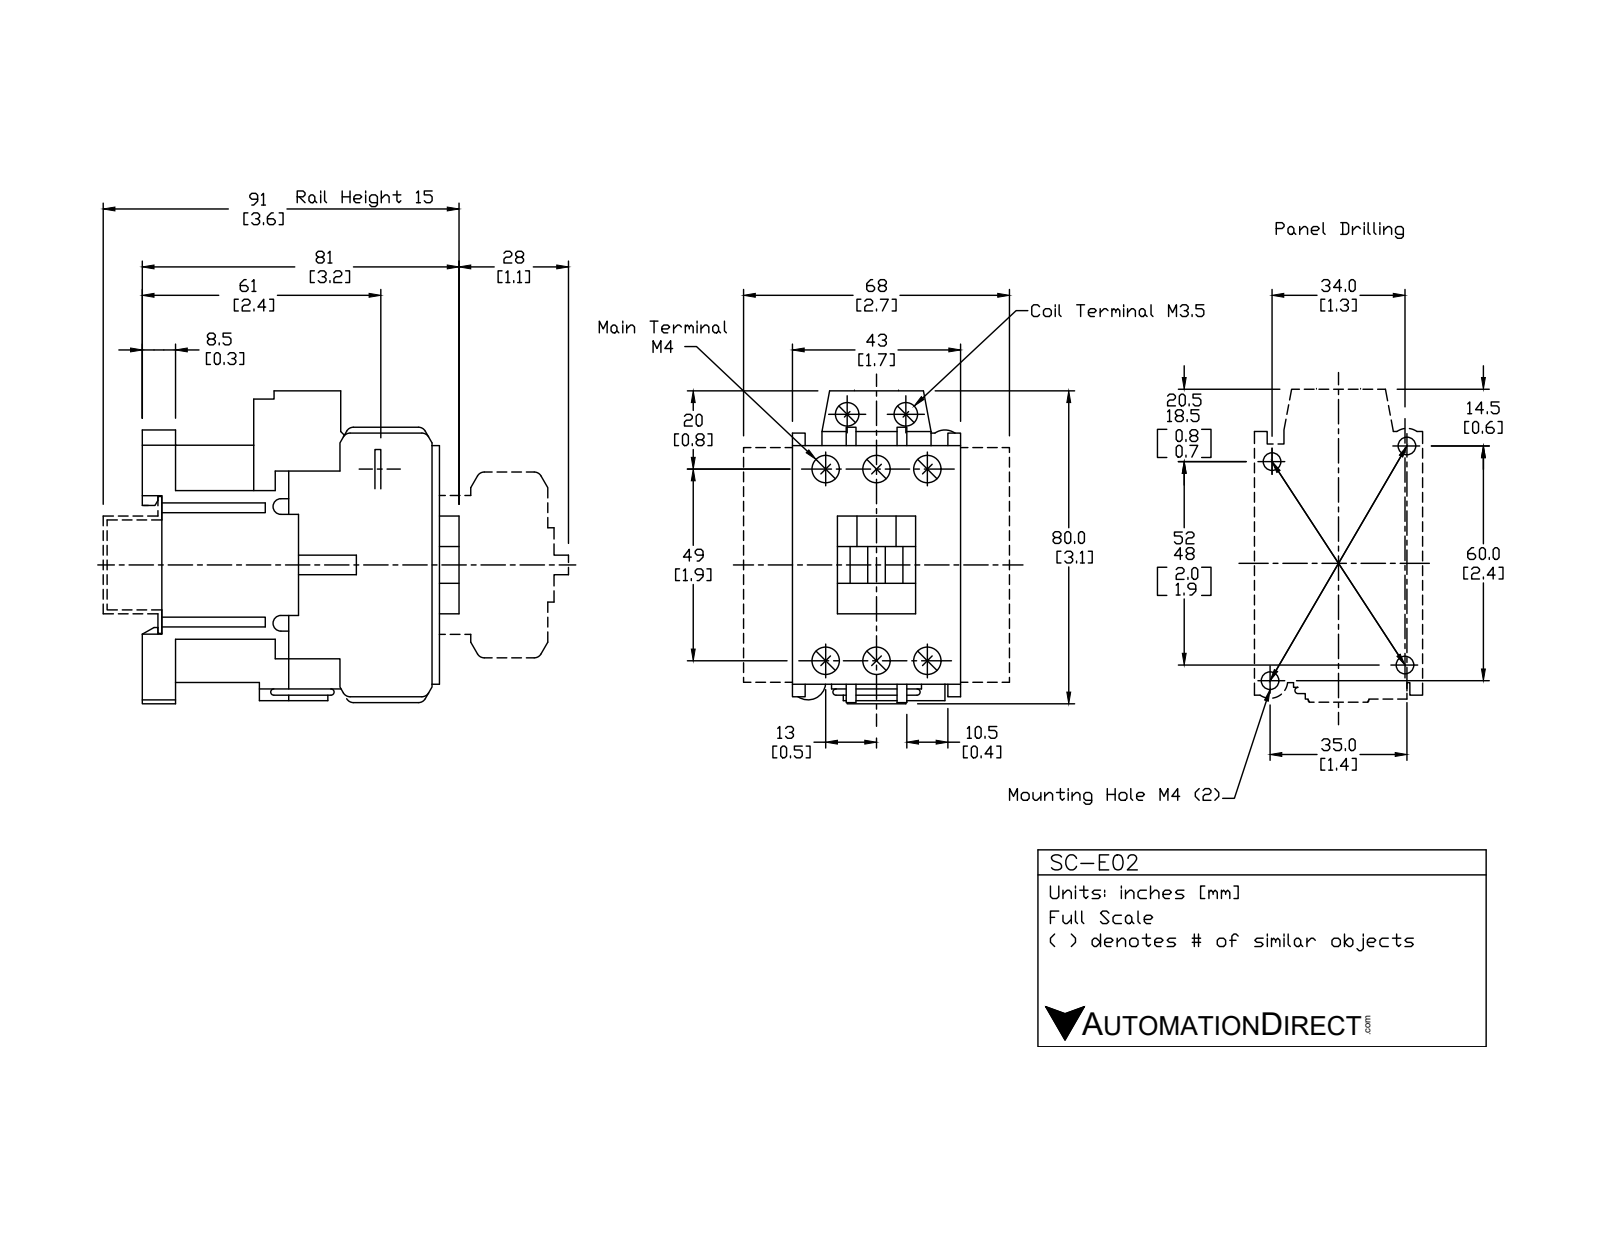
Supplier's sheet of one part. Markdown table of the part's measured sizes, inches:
| quantity | value |
| --- | --- |
| part name | SC-E02-220VAC |
| STEP written by | SolidWorks 2015 (AUTOMOTIVE_DESIGN) |
| units | inches |
| bodies | 1 solid, 1388 faces (1148 planar, 192 cylindrical, 48 other) |
| overall size | 3.189 × 3.189 × 1.693 |
| volume | 9.981 in³ |
| surface area | 65.66 in² |
| round holes (diameter × count) | 0.161 × 6, 0.276 × 6, 0.142 × 2, 0.177 × 2, 0.264 × 2, 0.063 × 1 |
| round bosses / shafts (diameter × count) | 0.299 × 6, 0.157 × 6, 0.28 × 2, 0.26 × 2, 0.138 × 2 |
| partial cylindrical surfaces (radius × count) | 0.059 × 32, 0.079 × 14, 0.02 × 10, 0.024 × 4, 0.089 × 4, 0.14 × 4, 0.163 × 2, 0.177 × 2 |
| main face-to-face distances | 1.693, 0.512, 0.413, 0.098, 0.925, 1.299, 0.64, 1.053, 0.61, 0.541 |
| hole center spacings | 0.512, 1.996, 1.929, 0.28, 0.301, 0.592, 0.625, 0.709 |
